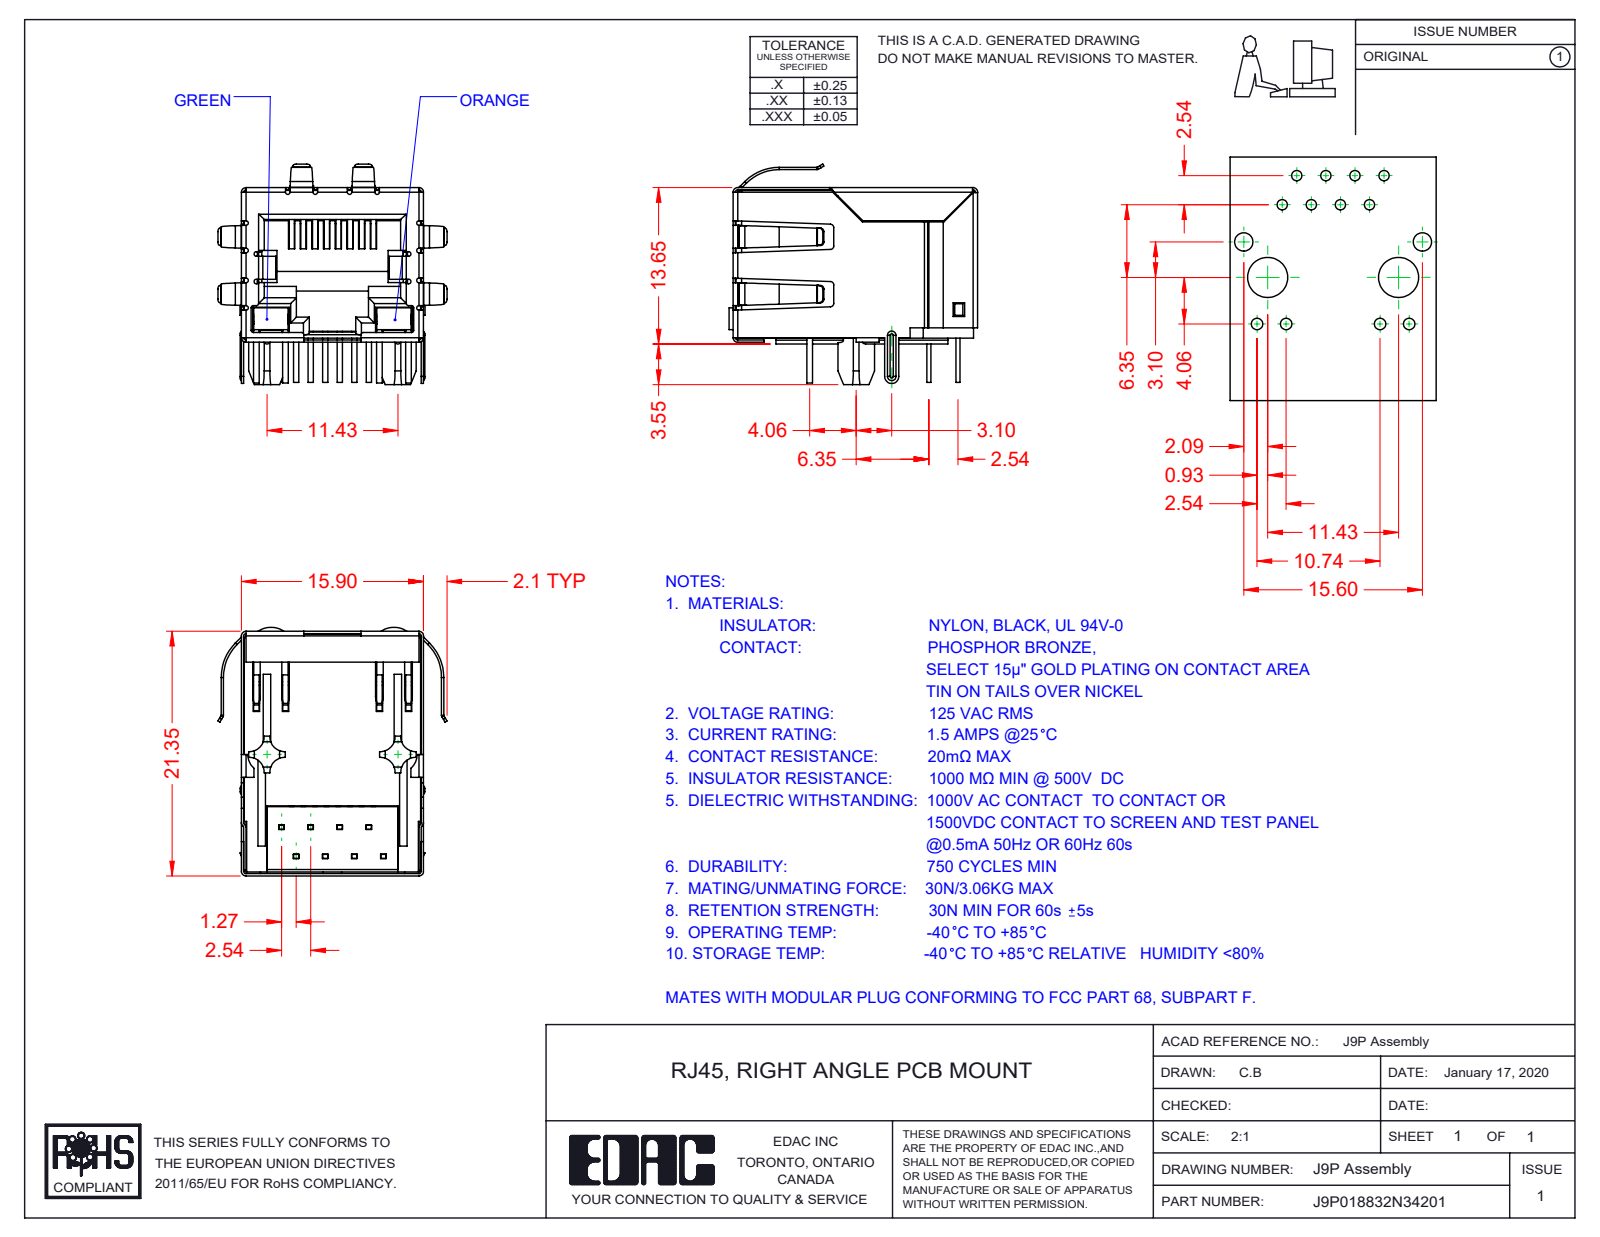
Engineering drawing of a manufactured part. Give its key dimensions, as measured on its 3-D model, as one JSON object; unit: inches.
{"part_name": "9P-LED Shield; 9P-LED Insulator; 9P-LED Contacts; J9P018832N34202 (+4 more)", "step_written_by": "SolidWorks 2016 (CONFIG_CONTROL_DESIGN)", "units": "inches", "bodies": {"solids": 13, "faces": 1472, "planar": 1042, "cylindrical": 336, "other": 94}, "overall_size": [0.854, 0.787, 0.758], "volume_in3": 0.164, "surface_area_in2": 11.65, "partial_cylinders_radius": [[0.008, 39], [0.02, 22], [0.012, 20], [0.016, 16], [0.051, 8], [0.009, 5], [0.004, 4], [0.012, 4]], "face_to_face_distances": [0.608, 0.618, 0.616, 0.014, 0.021, 0.61, 0.487, 0.024, 0.055, 0.023]}
